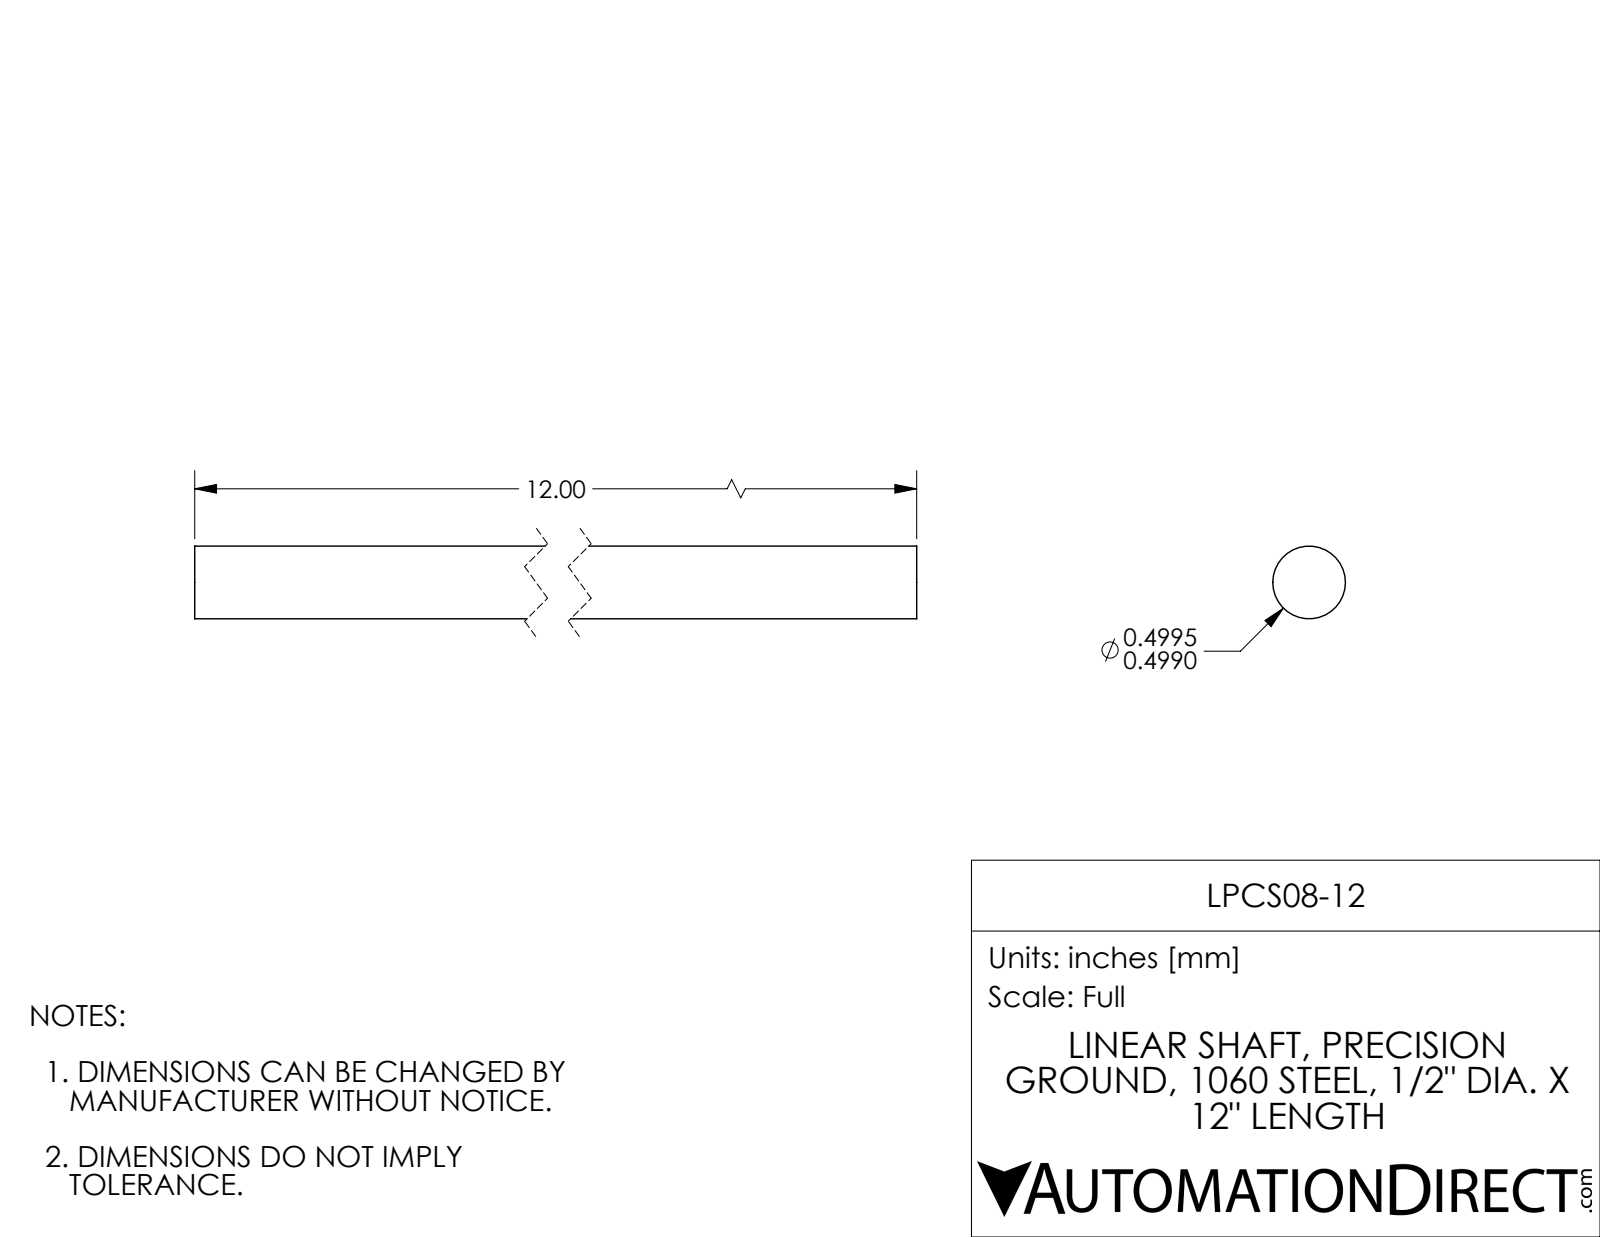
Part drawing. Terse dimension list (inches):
name: LPCS08-12
written by: SolidWorks 2017 (AUTOMOTIVE_DESIGN)
unit: in
bodies: 1 solid, 4 faces (2 planar, 2 cylindrical, 0 other)
size: 12 × 0.499 × 0.499
volume: 2.351 in³; area: 19.22 in²
bosses: 1× ⌀0.5
face distances: 12
